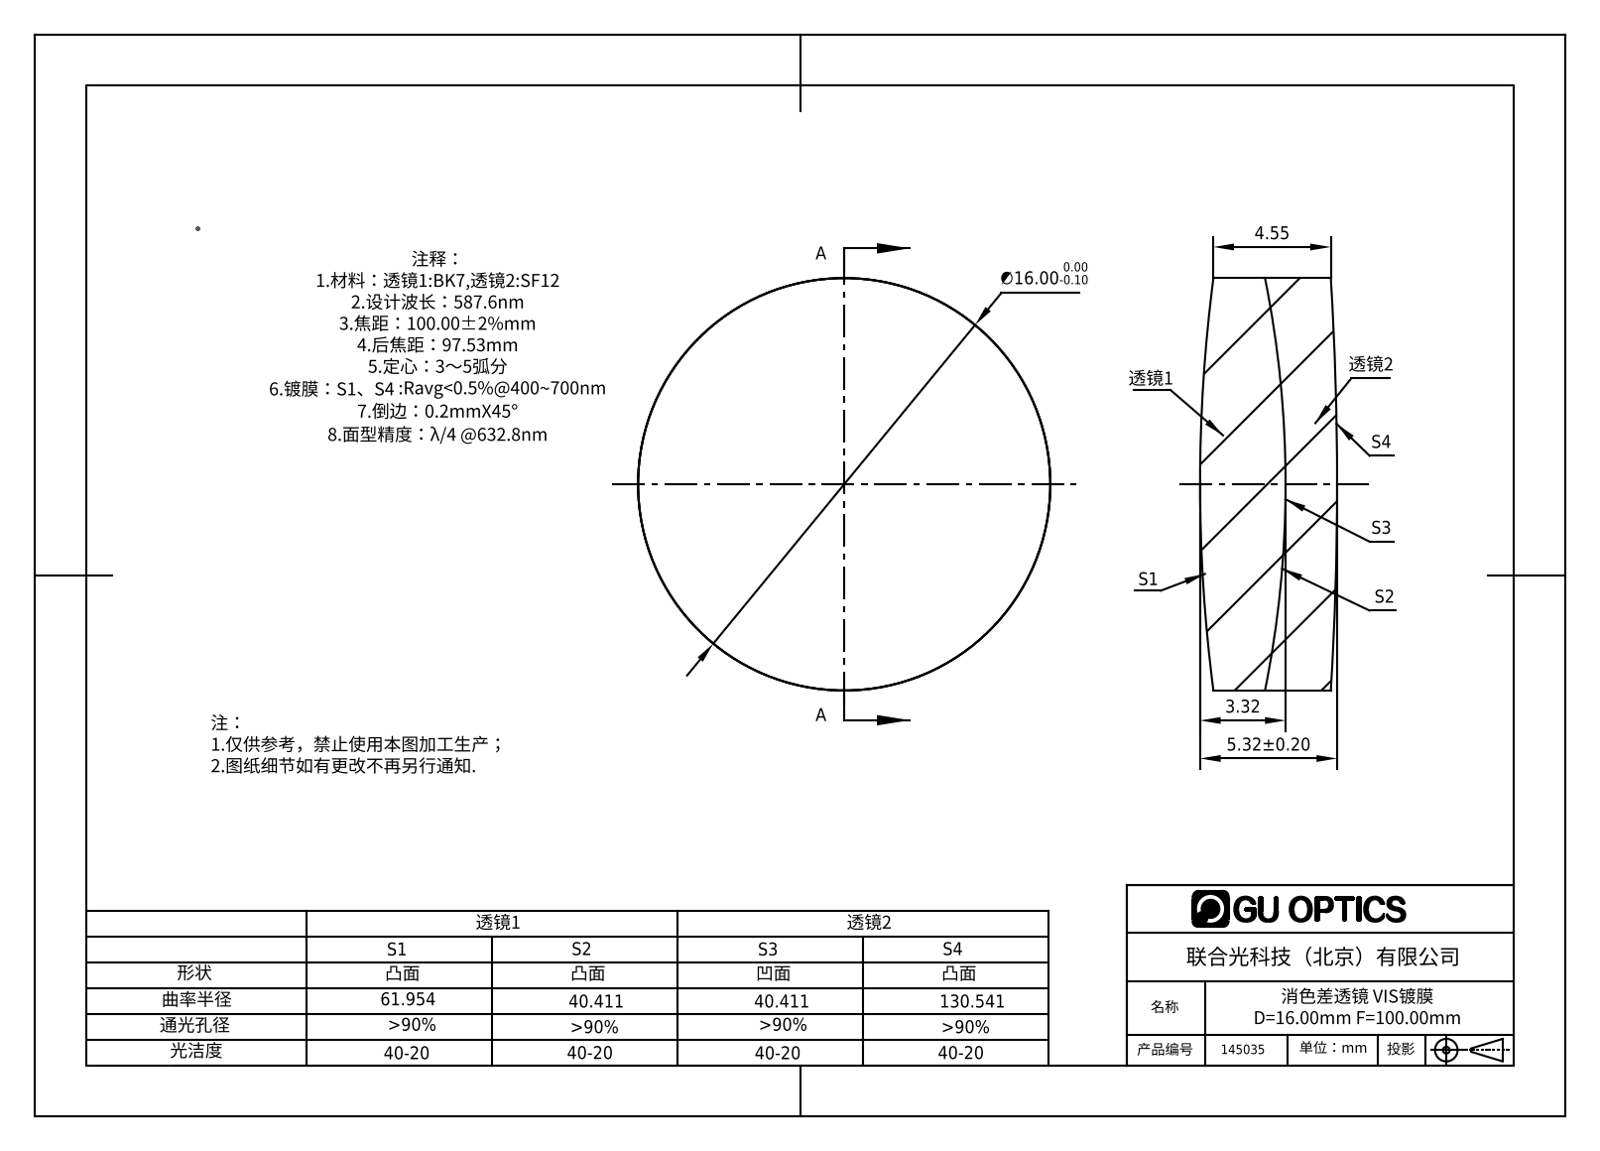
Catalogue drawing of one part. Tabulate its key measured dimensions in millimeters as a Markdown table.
| quantity | value |
| --- | --- |
| part name | 145035 |
| STEP written by | SolidWorks 2016 (AUTOMOTIVE_DESIGN) |
| units | millimeters |
| bodies | 2 solids, 12 faces (0 planar, 4 cylindrical, 8 other) |
| overall size | 16 × 16 × 5.32 |
| volume | 993 mm³ |
| surface area | 1 038 mm² |
| round bosses / shafts (diameter × count) | 16 × 1 |
